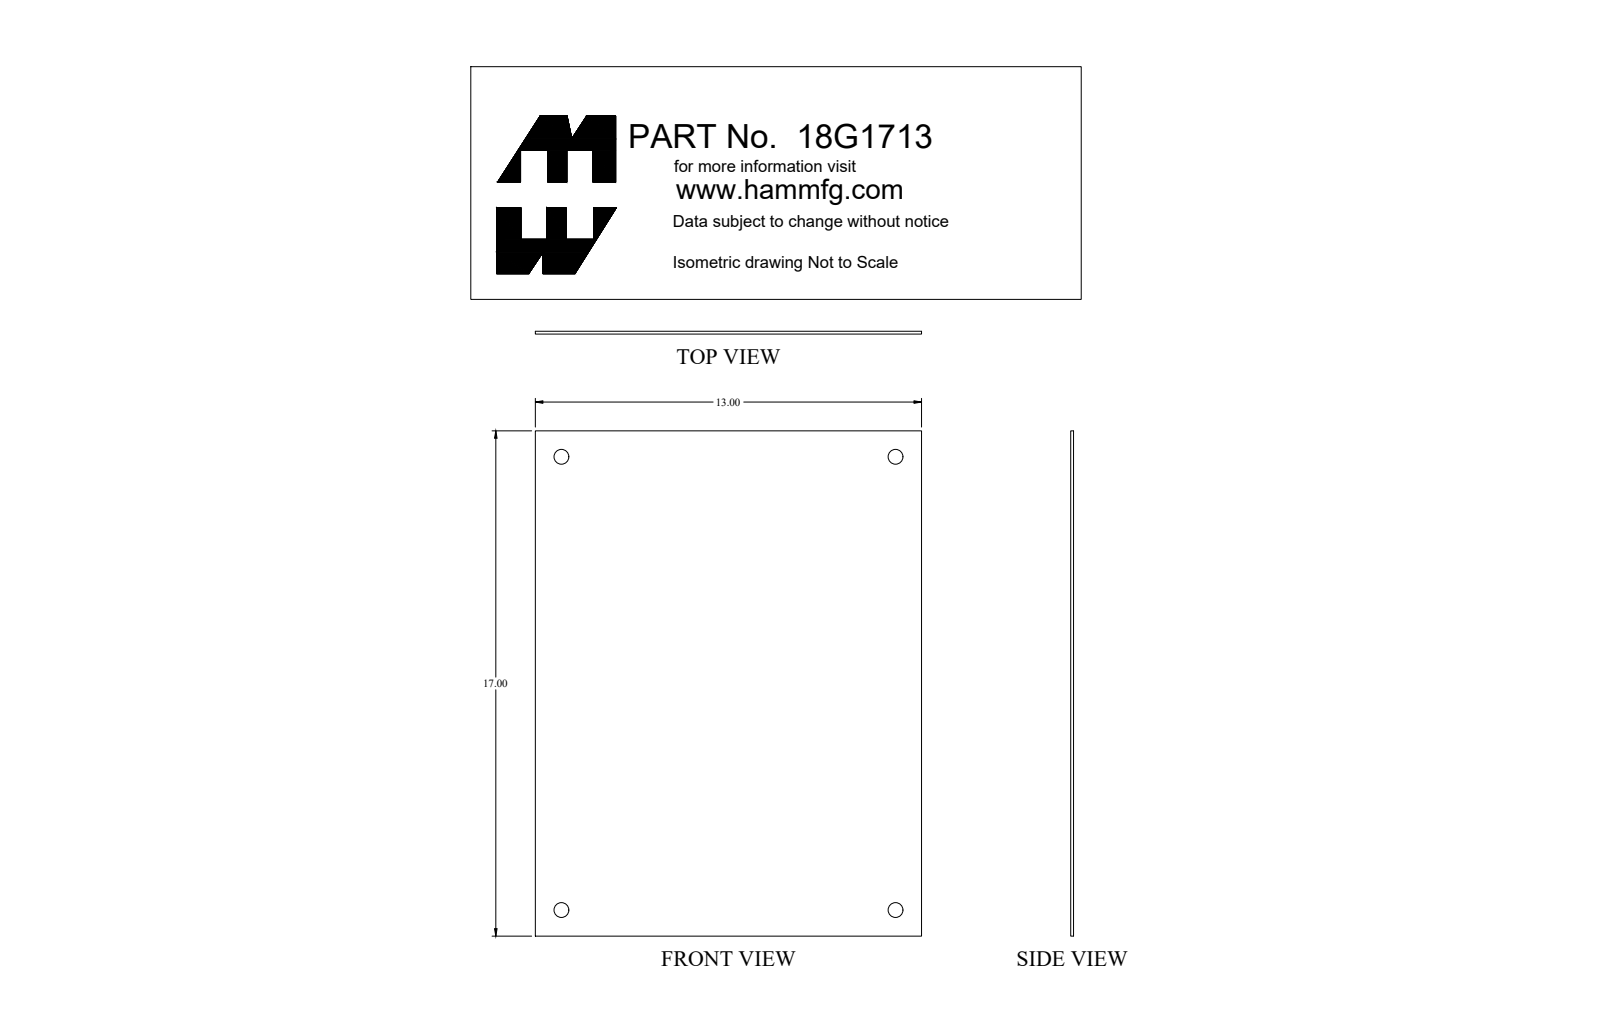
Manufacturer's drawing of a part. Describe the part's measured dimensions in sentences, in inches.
The part is named "18G1713". Its 3-D file was written by "SolidWorks 2018 (AUTOMOTIVE_DESIGN)". It is 1 solid with 10 faces: 6 planar, 4 cylindrical and 0 other. Overall it measures 17 by 13 by 0.095 inches. Its volume is 20.92 cubic inches and its surface area 446.7 square inches. Round holes: 4 of diameter 0.5. The main face-to-face distances are 0.095, 13, 17. The hole center spacings are 11.25, 15.25, 18.95.
